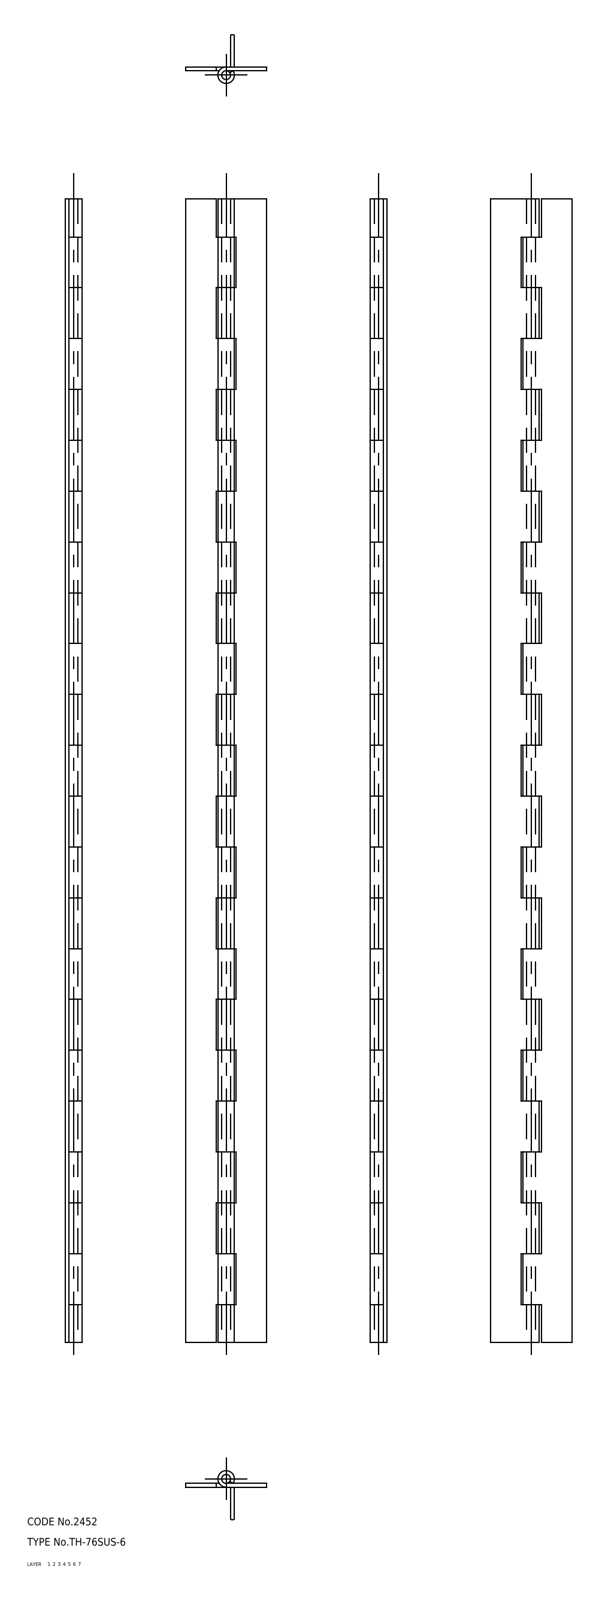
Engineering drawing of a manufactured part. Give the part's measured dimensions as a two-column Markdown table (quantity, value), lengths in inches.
| quantity | value |
| --- | --- |
| part name | shaft; hinge piece_B; hinge piece_A; TH_76SUS_6_15711_36 |
| STEP written by | CADfix (AUTOMOTIVE_DESIGN) |
| units | inches |
| bodies | 3 solids, 150 faces (0 planar, 0 cylindrical, 150 other) |
| overall size | 17.717 × 1.26 × 0.256 |
| volume | 1.96 in³ |
| surface area | 71.25 in² |
